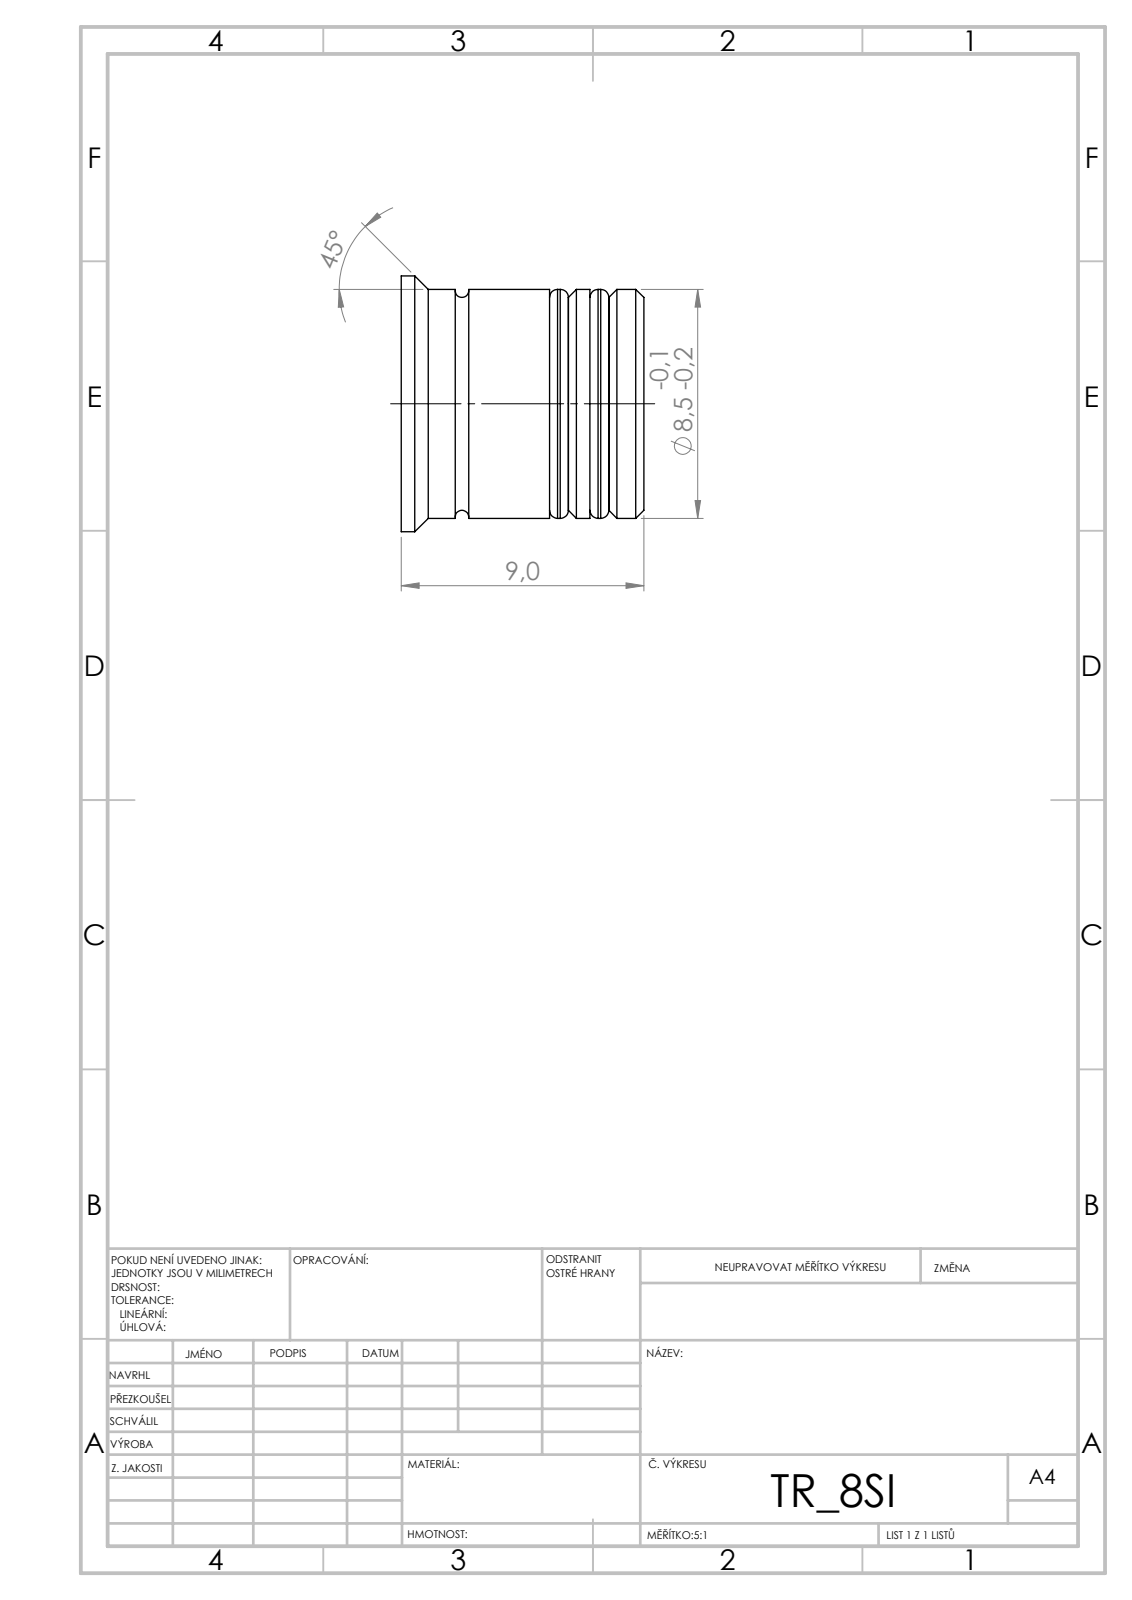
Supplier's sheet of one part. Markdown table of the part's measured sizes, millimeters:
| quantity | value |
| --- | --- |
| STEP written by | SolidWorks 2019 (CONFIG_CONTROL_DESIGN) |
| units | millimeters |
| bodies | 3 solids, 72 faces (30 planar, 20 cylindrical, 22 other) |
| overall size | 9.5 × 9.5 × 9 |
| volume | 550 mm³ |
| surface area | 703 mm² |
| round bosses / shafts (diameter × count) | 9.5 × 1, 8.5 × 1, 7.9 × 1, 5.5 × 1 |
| main face-to-face distances | 1.5, 0.7, 5.5, 2, 3.5, 2.2, 0.8, 1.3, 2.8, 1 |
